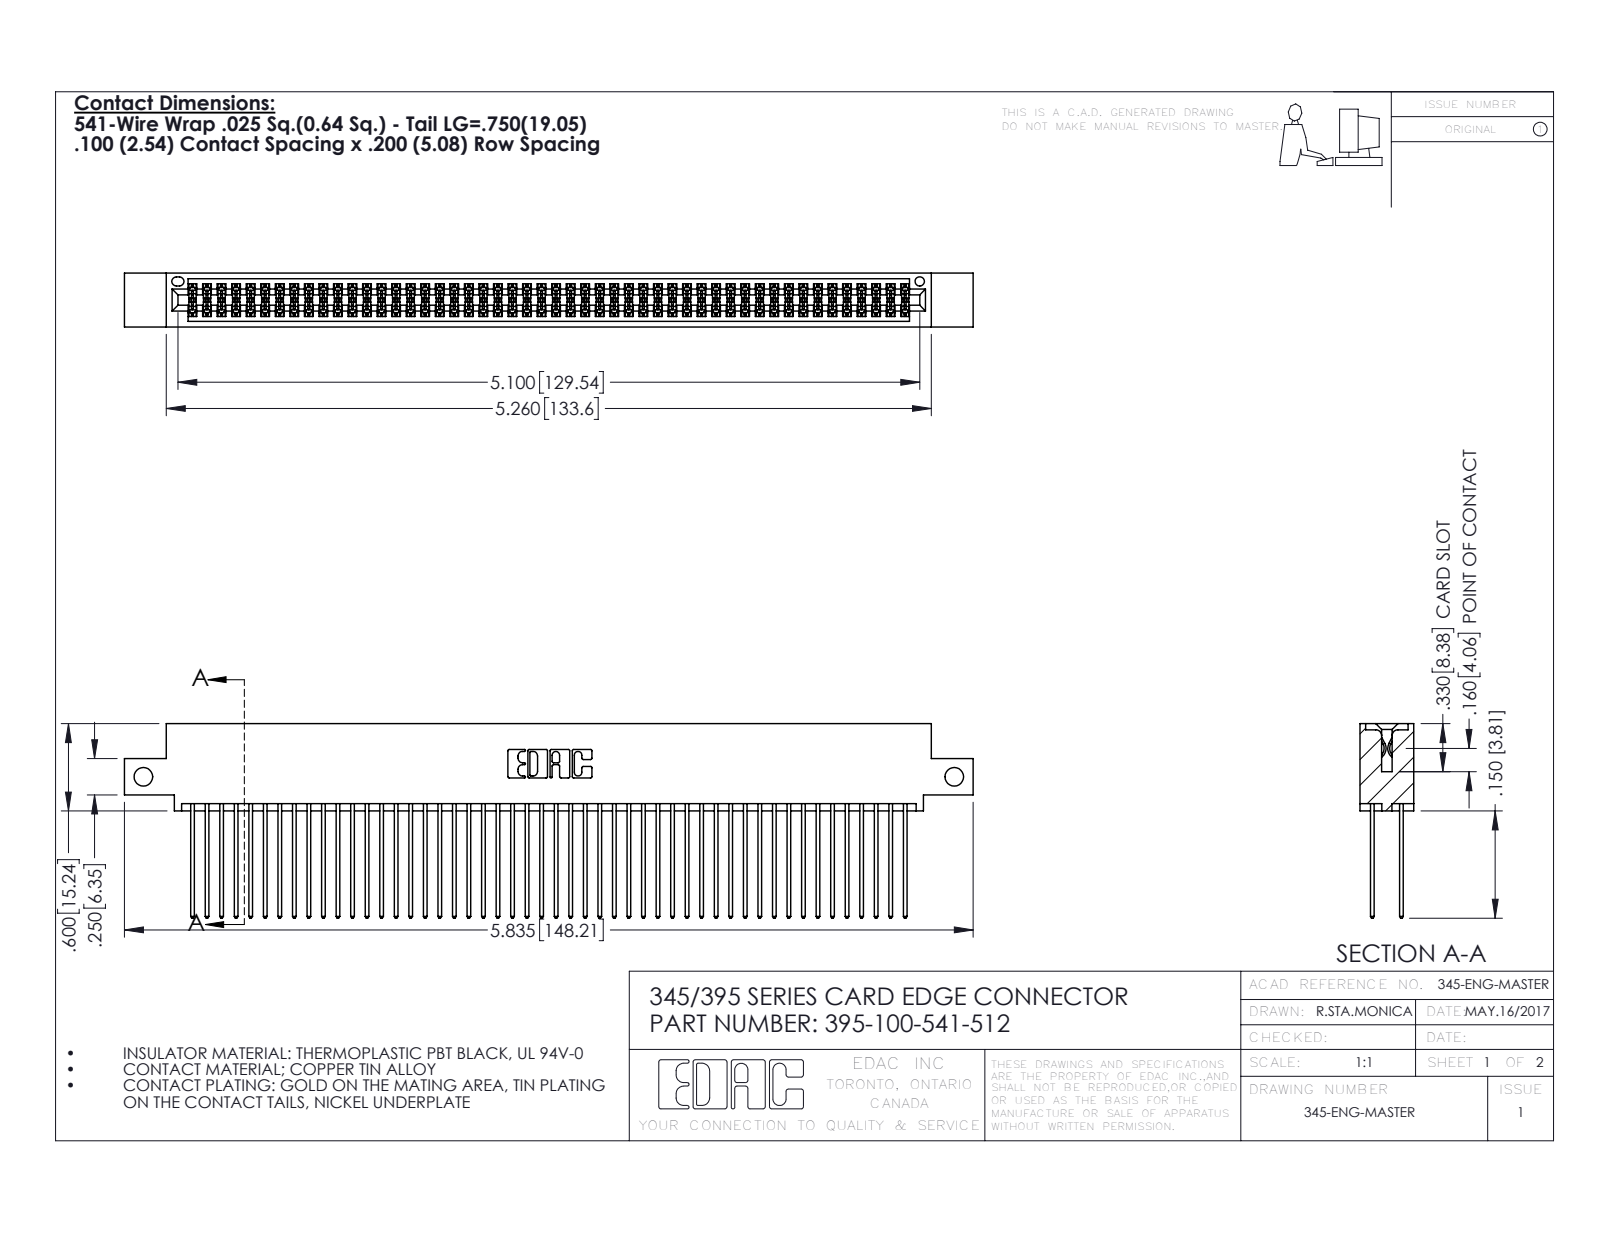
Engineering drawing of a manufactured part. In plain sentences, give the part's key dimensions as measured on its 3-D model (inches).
The part is named "345-292-001_345-293-141; 395-100-541-512; 345 Part_0.110 Offset - Side Mount". Its 3-D file was written by "SolidWorks 2016 (CONFIG_CONTROL_DESIGN)". It is 101 solids with 5130 faces: 3384 planar, 1746 cylindrical and 0 other. Overall it measures 5.835 by 1.337 by 0.37 inches. Its volume is 0.908 cubic inches and its surface area 38.46 square inches. Round holes: 2 of diameter 0.128, 1 of diameter 0.064. Partial cylindrical surfaces (rounded edges, fillets, slot ends): 150 of radius 0.006, 100 of radius 0.01, 22 of radius 0.01, 6 of radius 0.007, 6 of radius 0.031, 3 of radius 0.026, 2 of radius 0.014, 2 of radius 0.019. The main face-to-face distances are 0.072, 0.298, 0.2, 0.098, 0.272, 0.025, 0.225, 0.37, 0.175, 0.149. The hole center spacings are 5.575.
